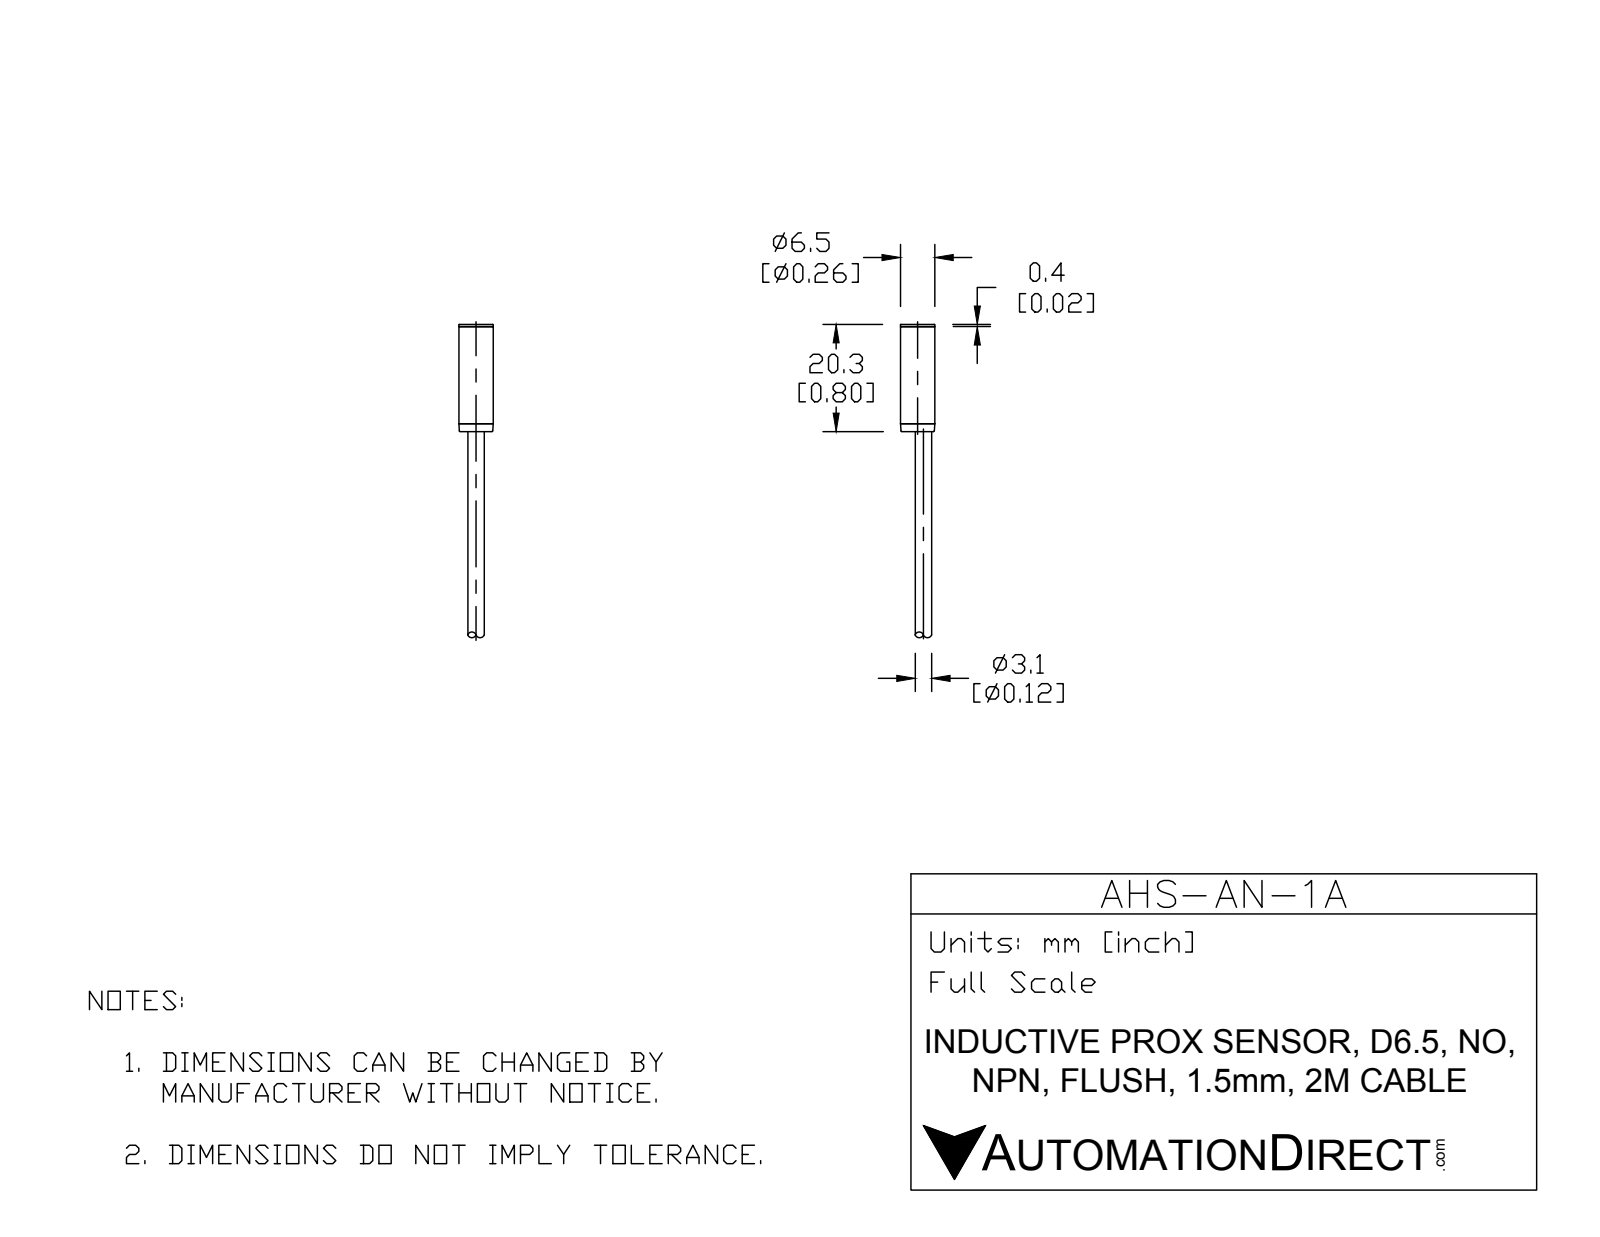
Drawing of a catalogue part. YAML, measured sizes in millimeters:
part_name: "AHS-AN-1A"
step_written_by: "SolidWorks 2015 (CONFIG_CONTROL_DESIGN)"
units: millimeters
bodies: {solids: 2, faces: 17, planar: 5, cylindrical: 6, other: 6}
overall_size: [70.3, 6.5, 6.5]
volume: 1050
surface_area: 979
round_bosses_or_shafts:
  - {diameter: 6.5, count: 1}
  - {diameter: 3.1, count: 1}
face_to_face_distances: [20.3, 50, 70.3, 69.9, 19.9, 0.4]
